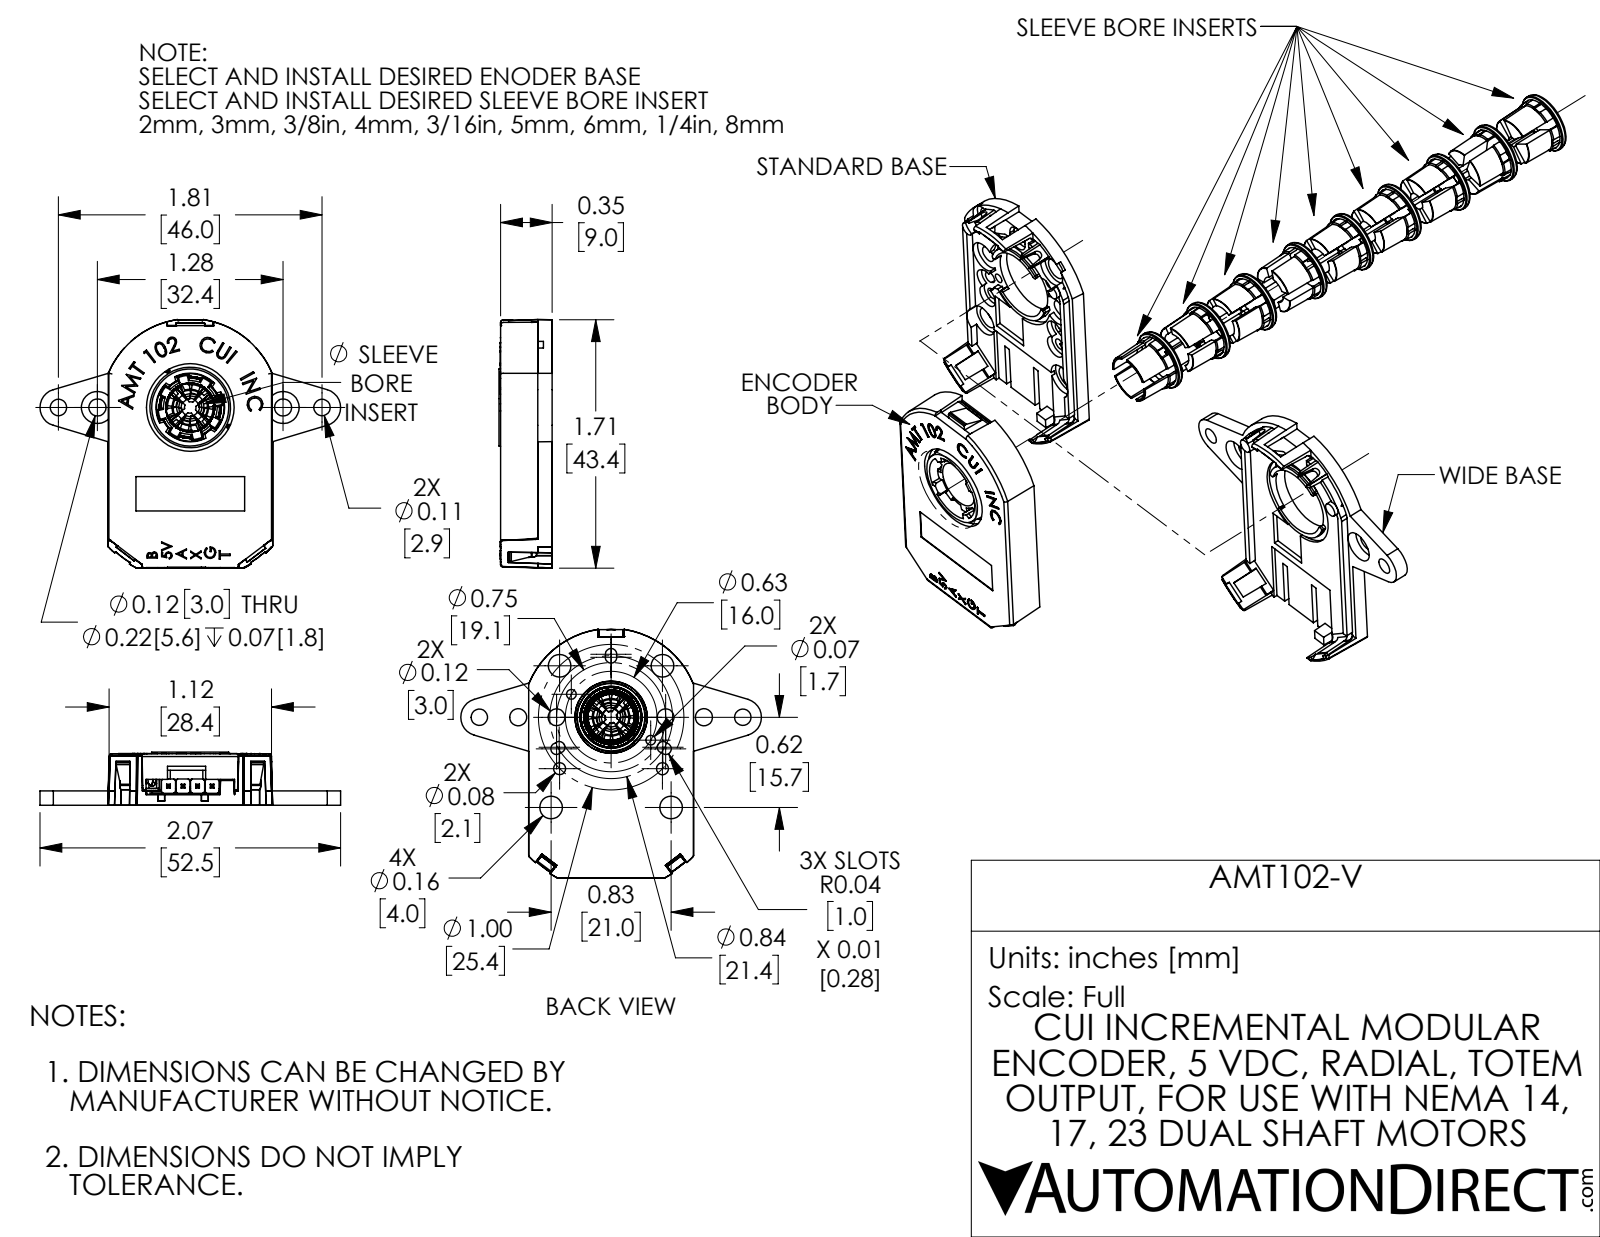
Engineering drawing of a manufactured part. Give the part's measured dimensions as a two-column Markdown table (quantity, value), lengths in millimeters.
| quantity | value |
| --- | --- |
| part name | CUI_cui_amt102s from 112s-0048-2000-w 4b r1 |
| STEP written by | SolidWorks 2017 (AUTOMOTIVE_DESIGN) |
| units | millimeters |
| bodies | 23 solids, 5630 faces (4264 planar, 552 cylindrical, 814 other) |
| overall size | 137.8 × 116.2 × 43.4 |
| volume | 10 100 mm³ |
| surface area | 19 210 mm² |
| round holes (diameter × count) | 1.6 × 4, 4 × 4, 5.8 × 4, 0.7 × 2, 0.8 × 2, 1.7 × 2, 2.1 × 2, 2.3 × 2, 2.9 × 2, 2.9 × 2, 3 × 2, 4.1 × 2 |
| round bosses / shafts (diameter × count) | 1.7 × 5, 1.5 × 4, 25.8 × 1, 22.2 × 1, 19.6 × 1, 11.8 × 1, 10.5 × 1, 9 × 1 |
| partial cylindrical surfaces (radius × count) | 1 × 40, 0.5 × 28, 0.4 × 14, 2 × 11, 2 × 6, 0.7 × 5, 0.8 × 4, 1 × 3 |
| main face-to-face distances | 1.4, 2.5, 45.5, 44.1, 4, 41.6, 0.3, 3.9, 0.7, 38.7 |
| hole center spacings | 9, 12.7, 18, 4.8, 5.4, 6.9, 8, 13.1 |
